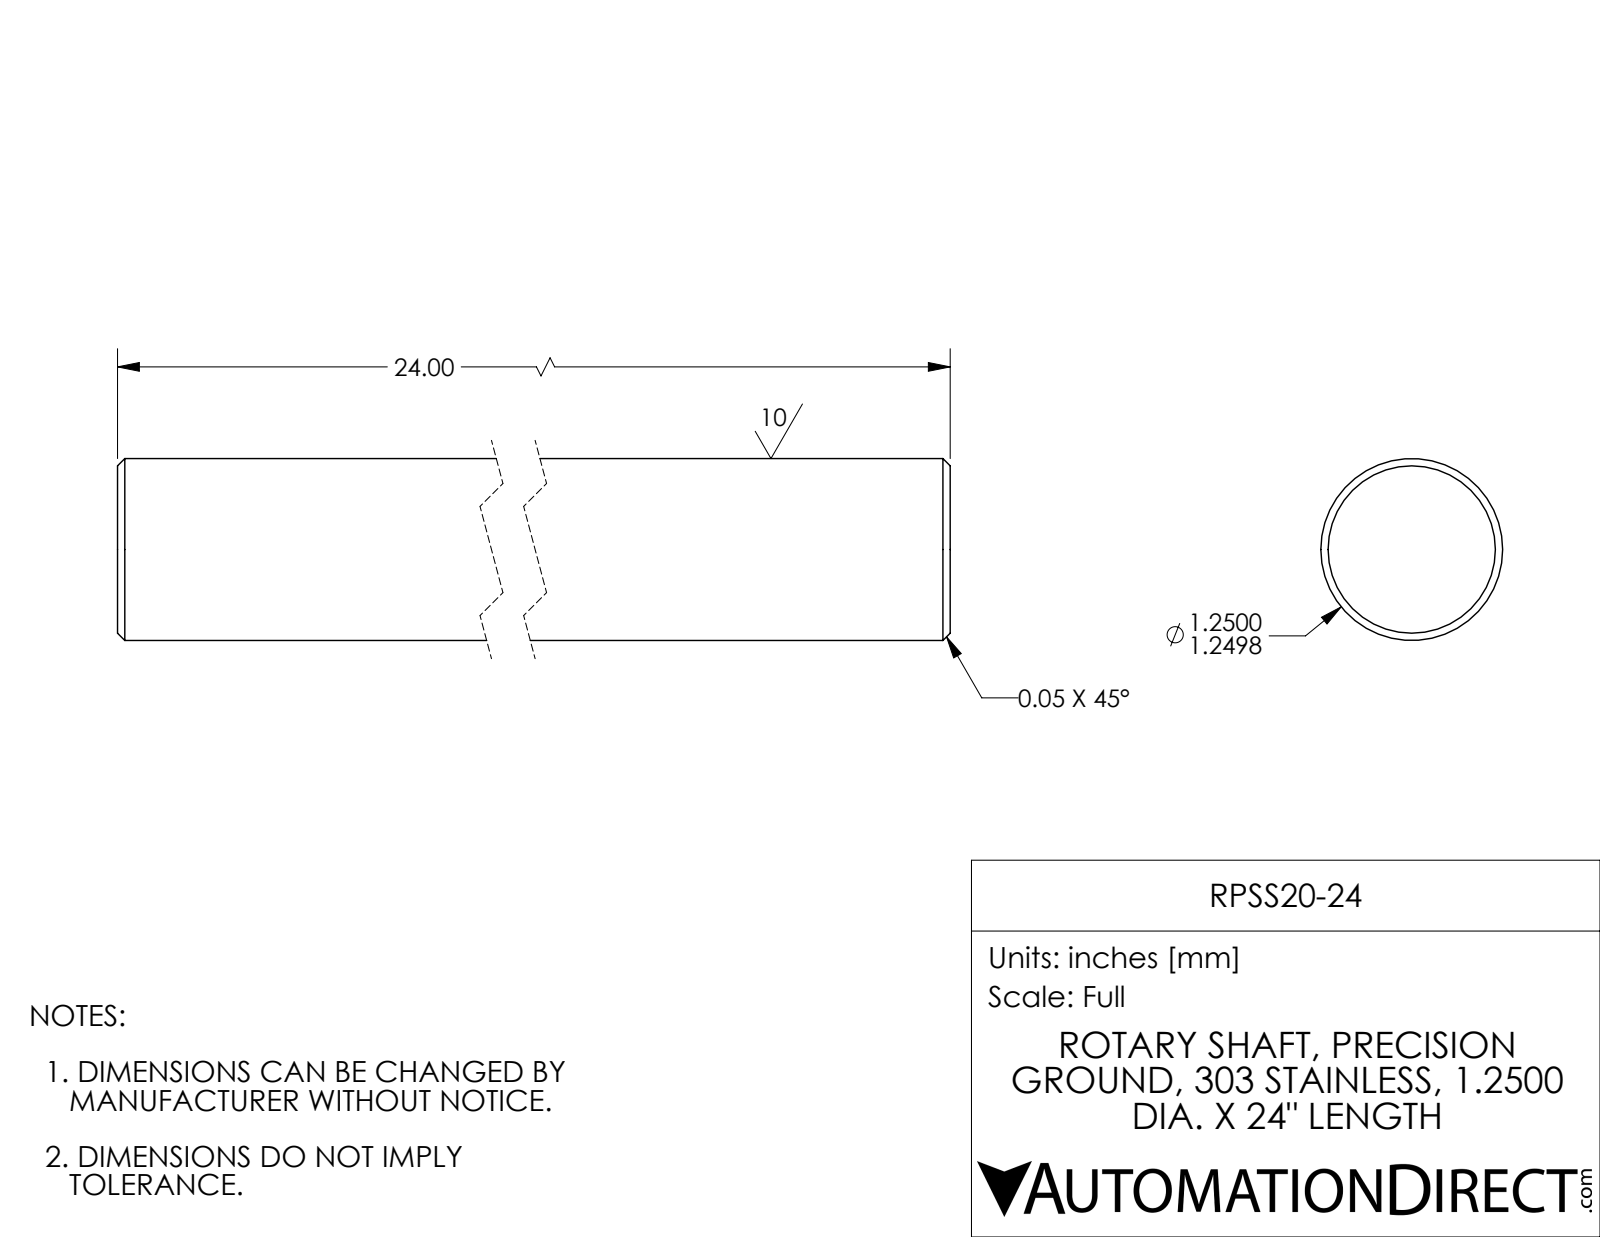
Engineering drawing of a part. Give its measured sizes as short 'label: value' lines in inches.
name: RPSS20-24
written by: SolidWorks 2017 (AUTOMOTIVE_DESIGN)
unit: in
bodies: 1 solid, 8 faces (2 planar, 2 cylindrical, 4 other)
size: 24 × 1.25 × 1.25
volume: 29.44 in³; area: 96.47 in²
bosses: 1× ⌀1.25
face distances: 24
